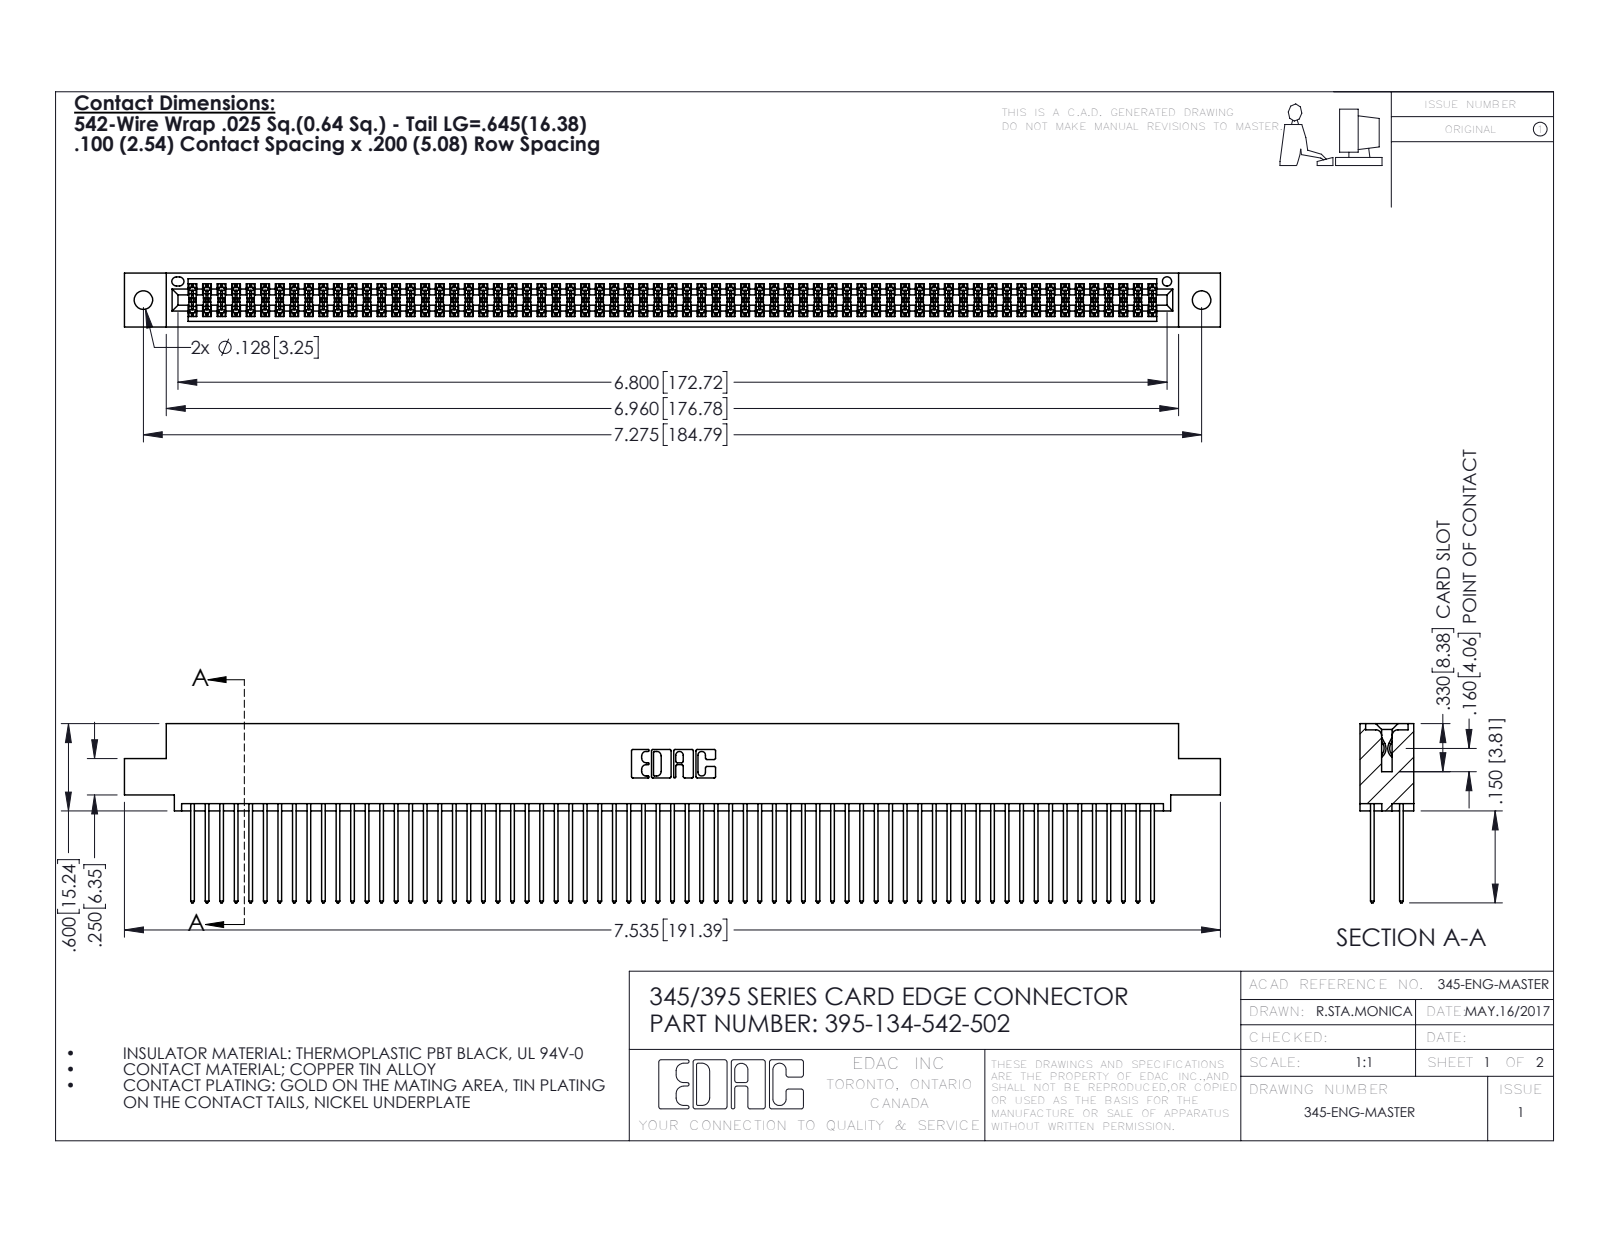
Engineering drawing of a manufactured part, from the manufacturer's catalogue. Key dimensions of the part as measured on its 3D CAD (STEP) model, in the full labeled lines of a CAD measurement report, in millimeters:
Part name (STEP PRODUCT): 345-292-001_345-293-142; 345 Part_0.110 Offset - 0.128 Dia; 395-134-542-502
STEP written by: SolidWorks 2016 (CONFIG_CONTROL_DESIGN)
Units: millimetres
Bodies: 135 solids, 6830 faces (4506 planar, 2324 cylindrical, 0 other)
Overall size (bounding box): 191.4 × 31.3 × 9.4
Volume: 19 340 mm³ · Surface area: 31 810 mm²
Round holes (diameter × count): ⌀3.3 ×2, ⌀1.6 ×1
Partial cylindrical surfaces — rounded edges, fillets, slot ends (radius × count): R0.2 ×201, R0.3 ×134, R0.3 ×22, R0.2 ×6, R0.8 ×6, R0.7 ×3, R0.4 ×2, R0.5 ×2
Main face-to-face distances: 7.6, 1.8, 5.1, 2.5, 6.9, 0.6, 5.7, 9.4, 4.4, 3.8
Hole centre spacings: 6.9, 178.8, 184.8
